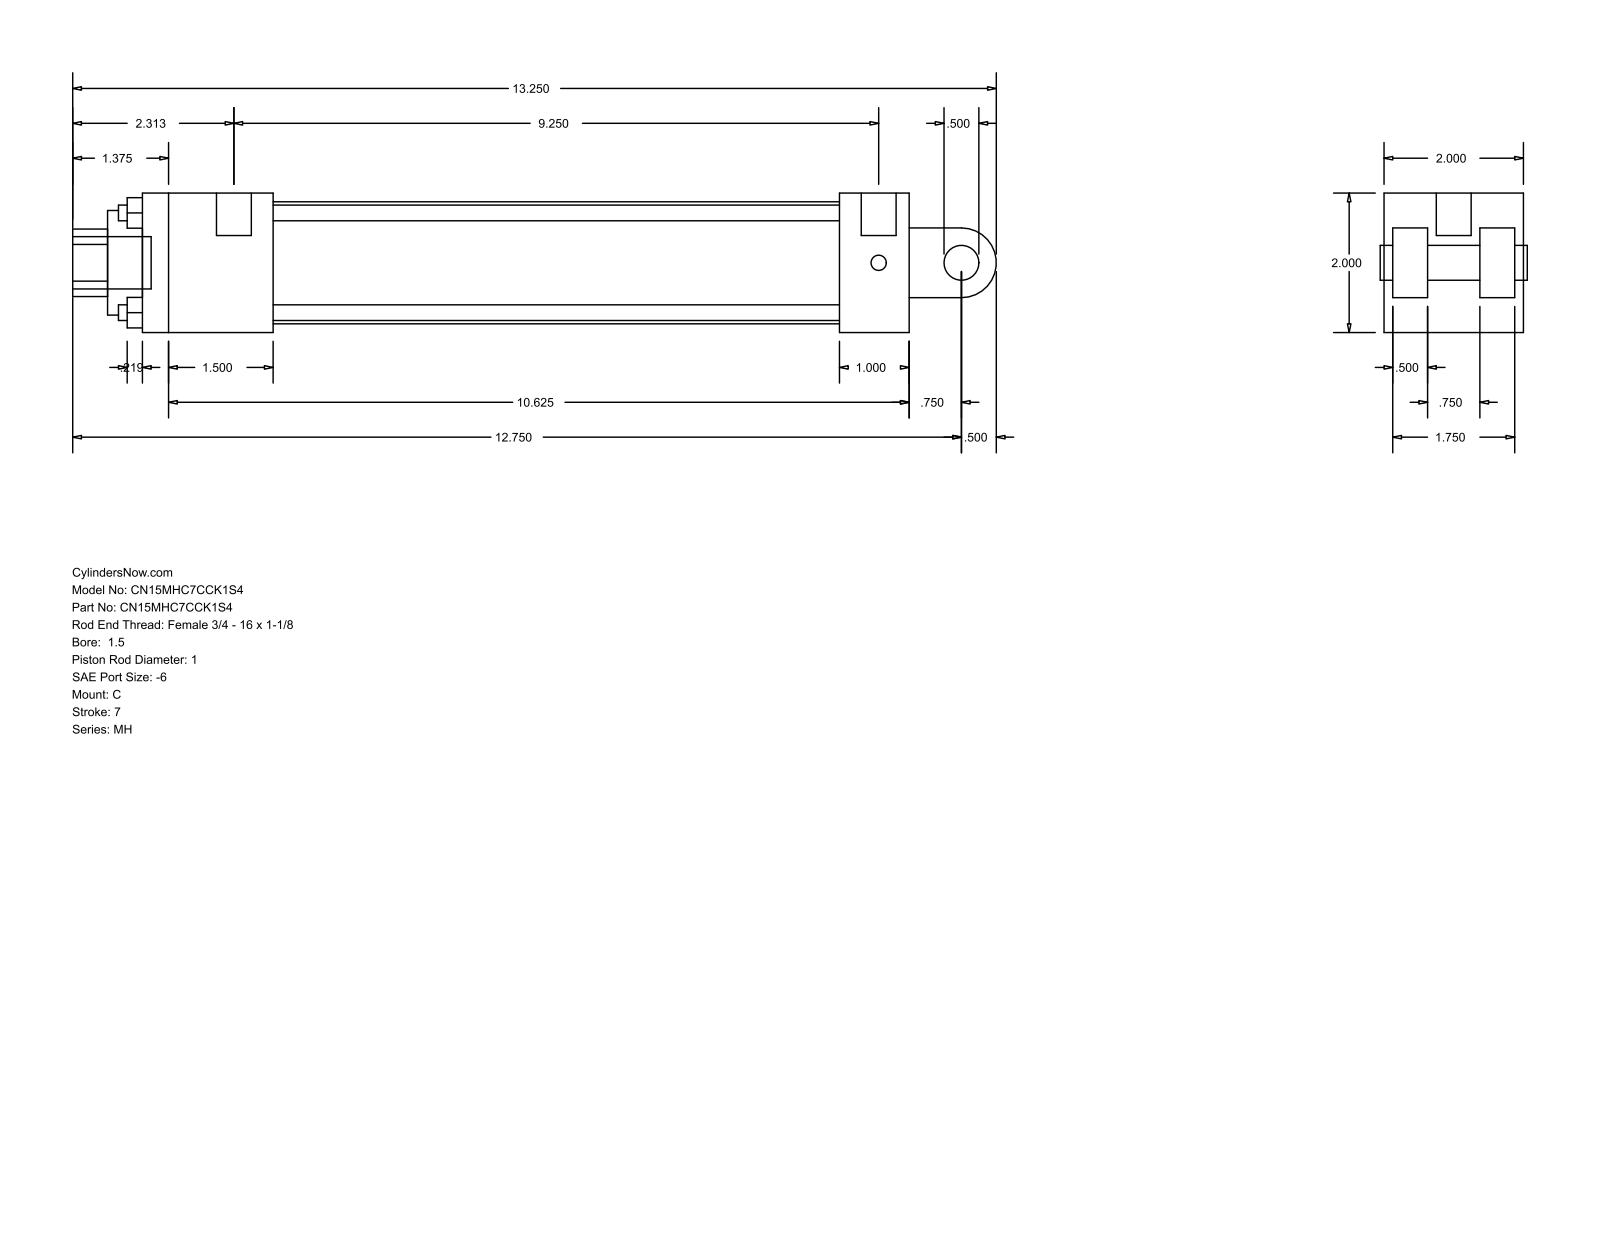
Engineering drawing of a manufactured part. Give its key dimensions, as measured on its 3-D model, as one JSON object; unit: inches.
{"part_name": "MH_C__0150_1", "step_written_by": "GSSL Pune (CONFIG_CONTROL_DESIGN)", "units": "inches", "bodies": {"solids": 0, "faces": 99, "planar": 70, "cylindrical": 29, "other": 0}, "overall_size": [13.25, 2, 2], "round_holes": [[0.225, 4], [0.219, 2], [0.5, 1], [1, 1], [1.5, 1], [1.75, 1]], "round_bosses_or_shafts": [[0.5, 2], [0.219, 2], [0.75, 1]], "partial_cylinders_radius": [[0.484, 1], [0.5, 1]], "face_to_face_distances": [2, 0.5, 1.875, 0.125, 0.625, 1, 1.375, 1.25, 11, 1.5], "hole_center_spacings": [1.011, 1.43, 2.022]}
